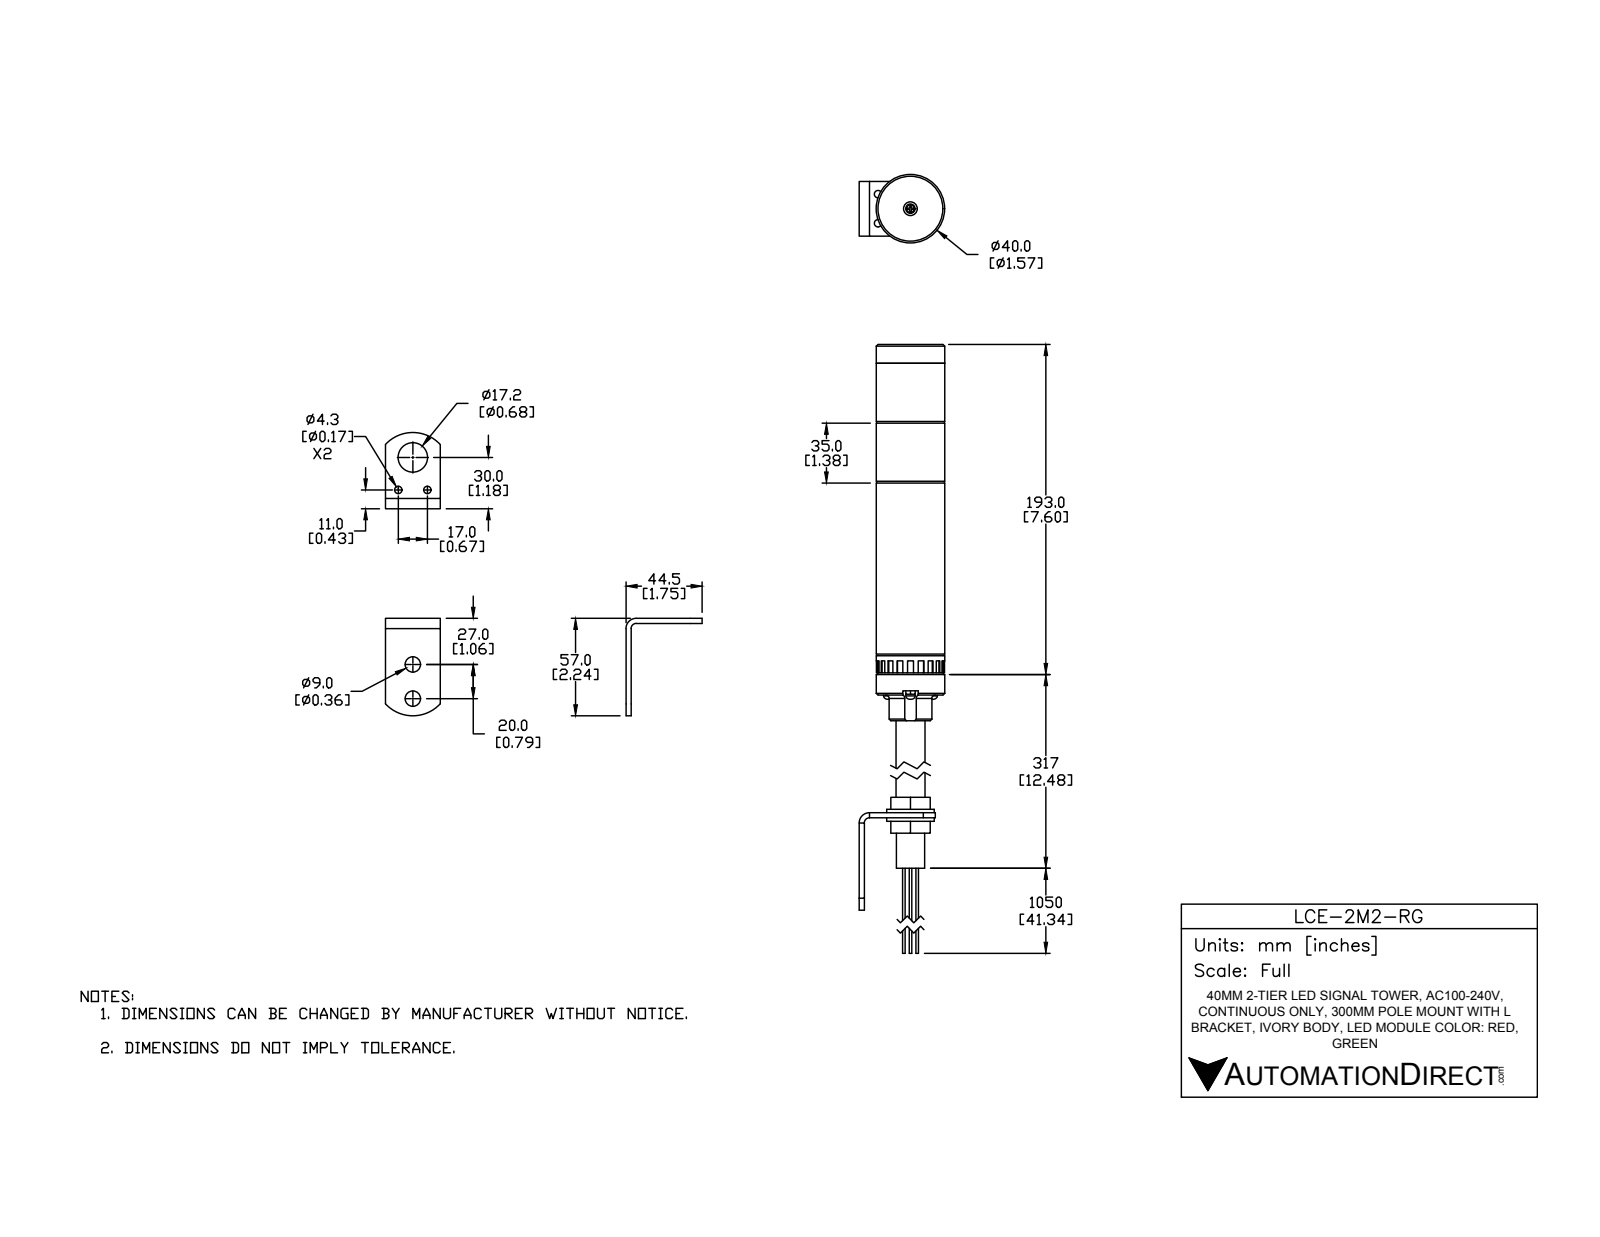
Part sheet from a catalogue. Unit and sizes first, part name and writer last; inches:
Units: inches
Overall size (bounding box): 24.055 × 1.969 × 1.575
Round holes (diameter × count): ⌀0.138 ×3, ⌀0.157 ×3, ⌀0.169 ×2, ⌀0.356 ×2, ⌀0.315 ×1, ⌀0.472 ×1, ⌀0.677 ×1, ⌀0.689 ×1, ⌀0.709 ×1
Round bosses / shafts (diameter × count): ⌀0.118 ×6, ⌀0.059 ×6, ⌀0.217 ×4, ⌀1.575 ×1, ⌀1.555 ×1, ⌀1.516 ×1, ⌀1.094 ×1, ⌀0.669 ×1
Partial cylindrical surfaces — rounded edges, fillets, slot ends (radius × count): R0.177 ×3, R0.858 ×2, R0.118 ×1, R0.236 ×1, R0.492 ×1
Main face-to-face distances: 0.039, 1.378, 0.433, 1.339, 3.976, 5.354, 4.409, 5.787, 7.126, 7.165
Hole centre spacings: 0.591, 1.023, 0.819, 0.24, 0.669, 0.673, 0.787, 0.791
Volume: 19.32 in³ · Surface area: 182 in²
Bodies: 32 solids, 373 faces (239 planar, 114 cylindrical, 20 other)
Part name (STEP PRODUCT): LCE-2M2-RG
STEP written by: SolidWorks 2016 (AUTOMOTIVE_DESIGN)
